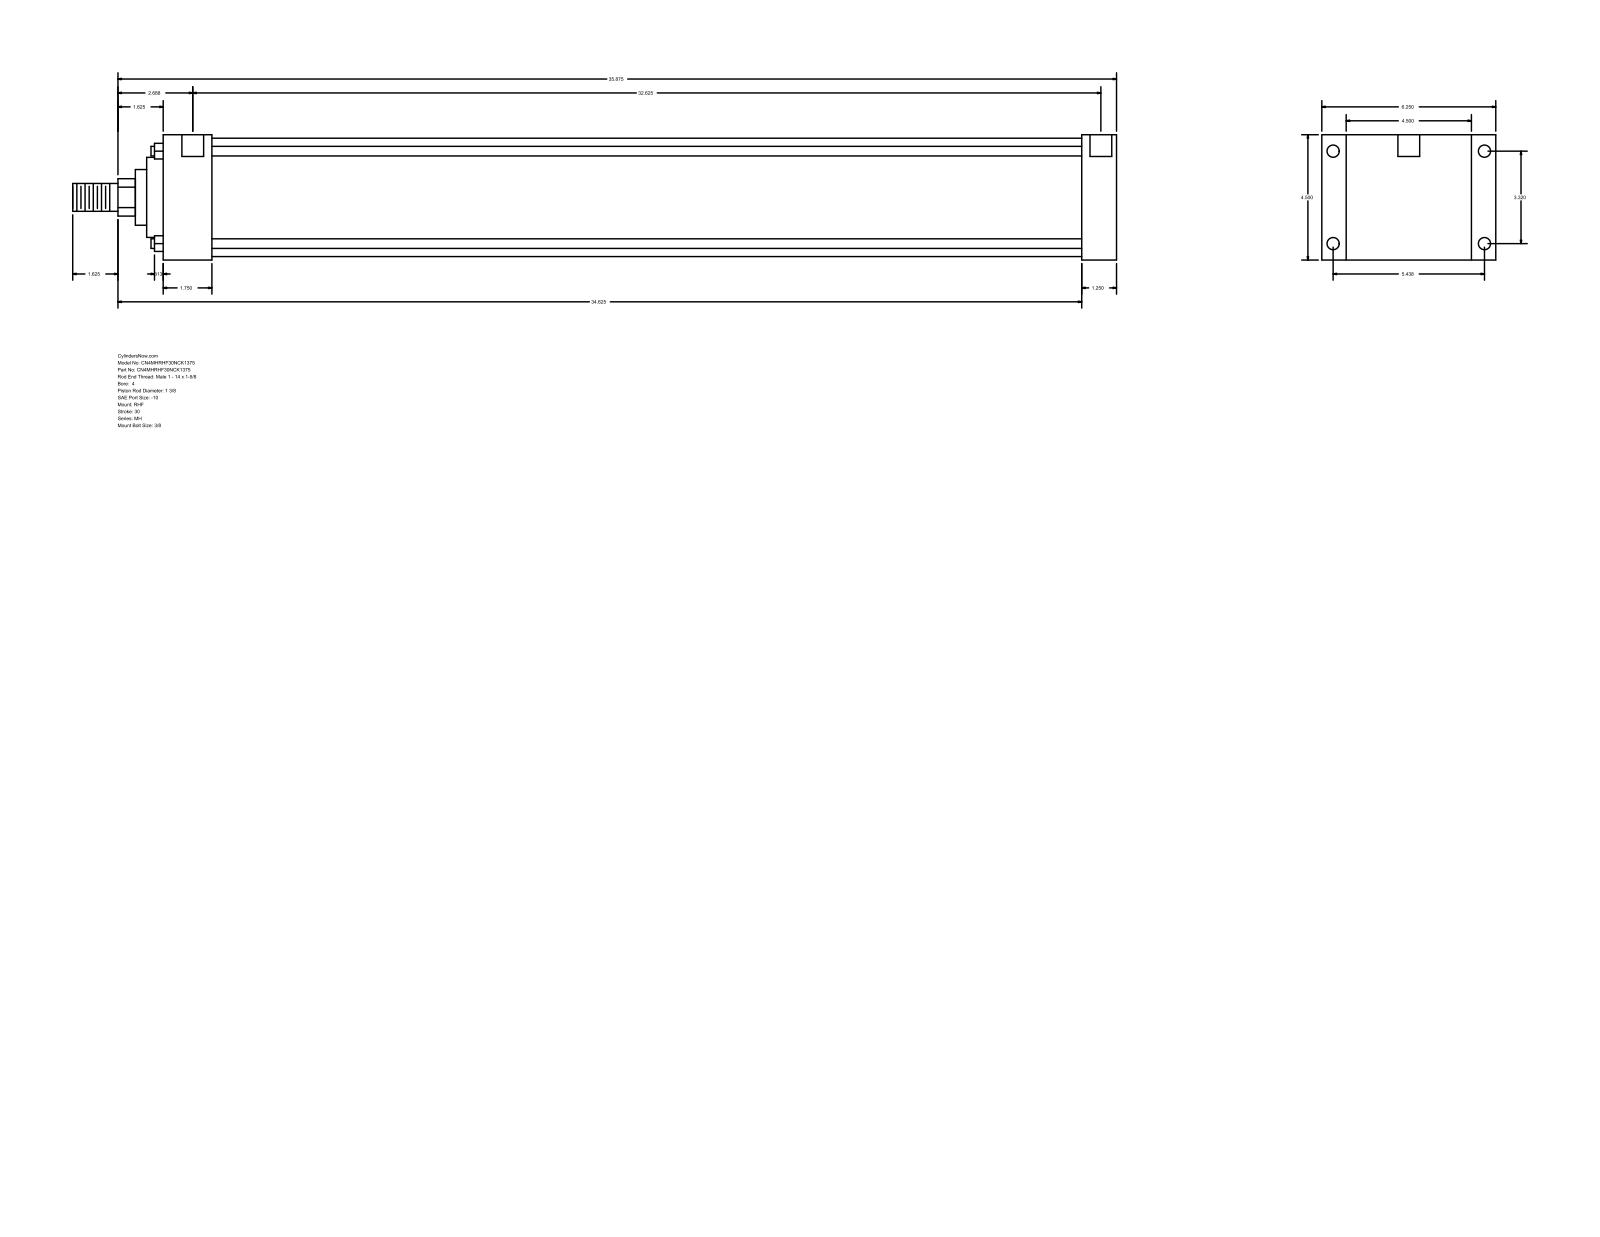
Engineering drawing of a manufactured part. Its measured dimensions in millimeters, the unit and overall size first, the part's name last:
Units: millimetres
Overall size (bounding box): 952.5 × 158.75 × 114.3
Round holes (diameter × count): ⌀8.73 ×4, ⌀11.13 ×4, ⌀19.84 ×2
Round bosses / shafts (diameter × count): ⌀8.76 ×4, ⌀107.95 ×1, ⌀73.03 ×1, ⌀50.8 ×1, ⌀34.92 ×1, ⌀25.4 ×1
Partial cylindrical surfaces — rounded edges, fillets, slot ends (radius × count): R17.06 ×1
Main face-to-face distances: 114.3, 31.75, 838.21, 869.96, 22.23, 136.53, 44.45, 793.76, 825.51, 158.76
Hole centre spacings: 84.32, 138.12, 161.82, 831.85, 1.58, 1.59, 828.68, 830.26
Bodies: 0 solids, 90 faces (61 planar, 29 cylindrical, 0 other)
Part name (STEP PRODUCT): MH_RHF__0400_1.375
STEP written by: GSSL Pune (CONFIG_CONTROL_DESIGN)
